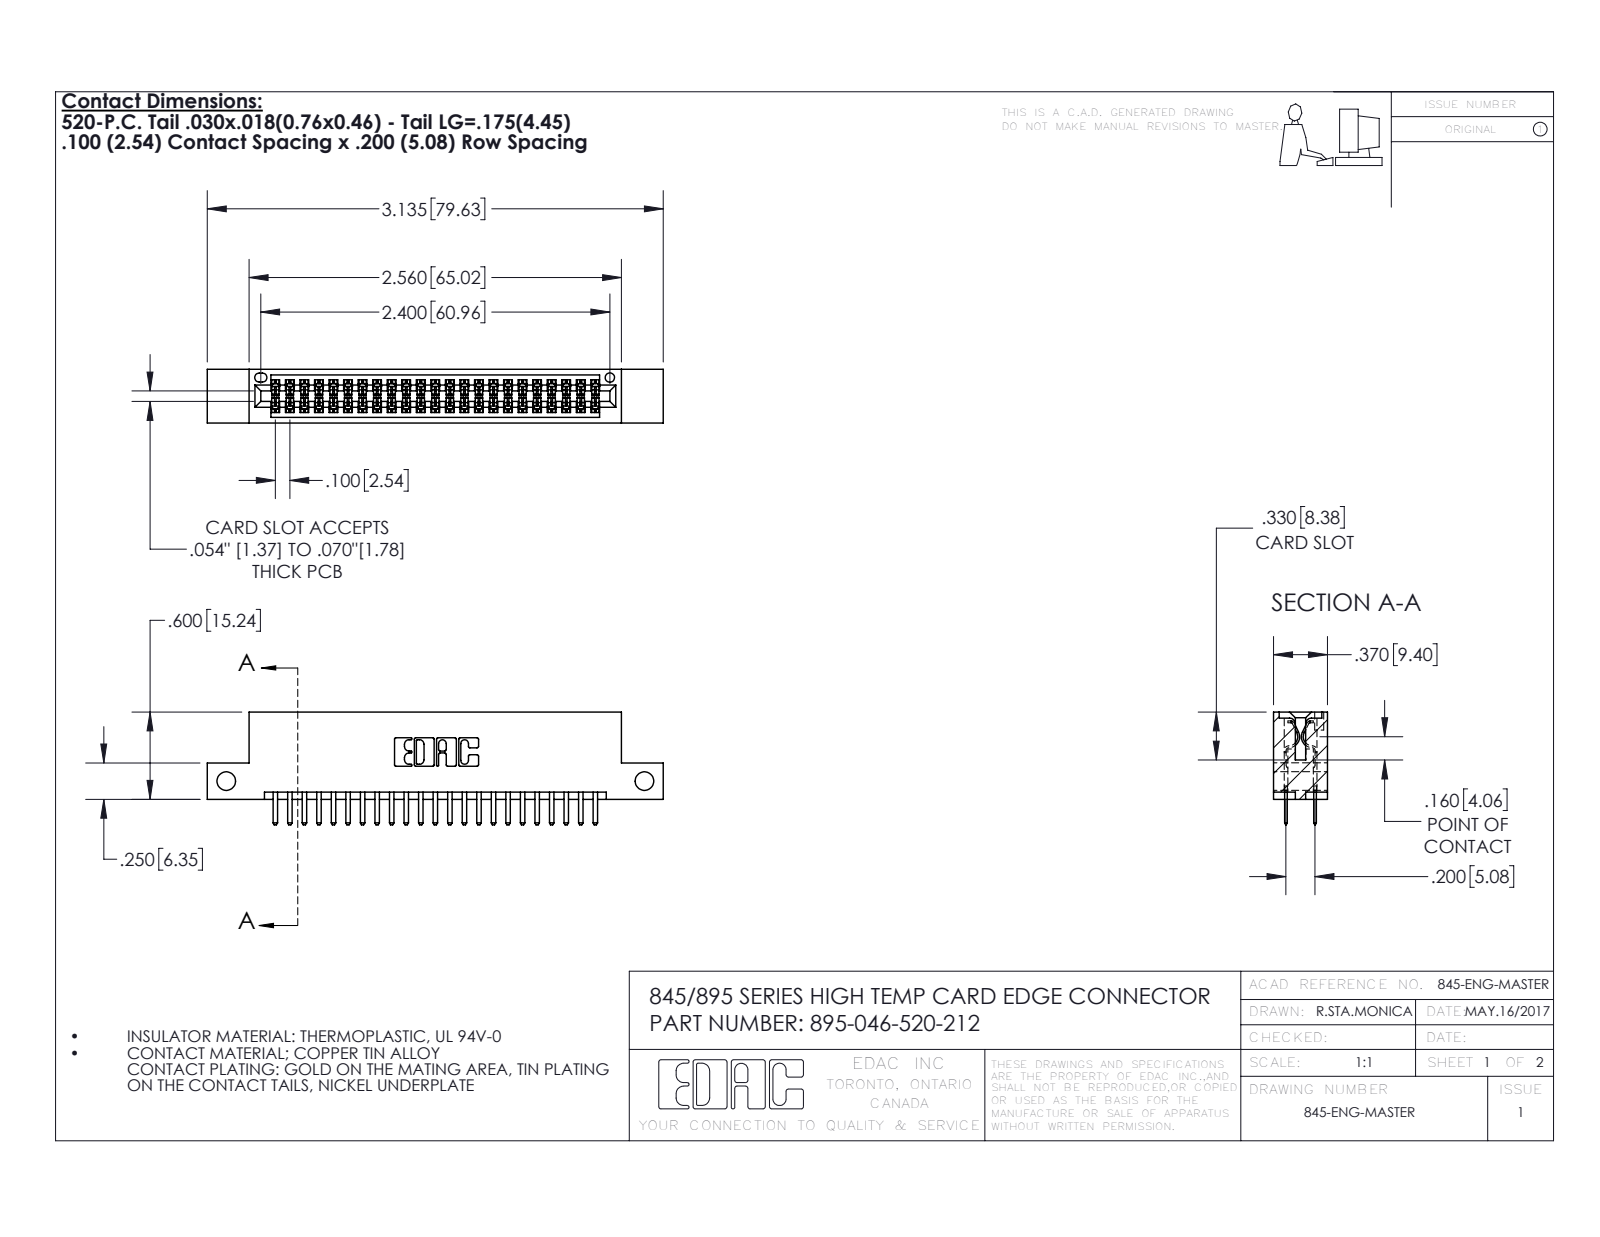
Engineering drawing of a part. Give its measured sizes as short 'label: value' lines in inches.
name: 345-292-001_345-293-120; 345 Part_Flush Mounting Lugs - Side Mount; 395-046-520-212
written by: SolidWorks 2016 (CONFIG_CONTROL_DESIGN)
unit: in
bodies: 47 solids, 2610 faces (1690 planar, 920 cylindrical, 0 other)
size: 3.135 × 0.775 × 0.37
volume: 0.455 in³; area: 16.22 in²
holes: 2× ⌀0.128, 1× ⌀0.064
rounds: 69× R0.006, 50× R0.01, 22× R0.01, 6× R0.007, 6× R0.031, 3× R0.026, 2× R0.014, 2× R0.019
face distances: 0.2, 0.298, 0.072, 0.37, 0.098, 0.272, 0.025, 0.225, 0.022, 0.072
hole spacings: 2.875
